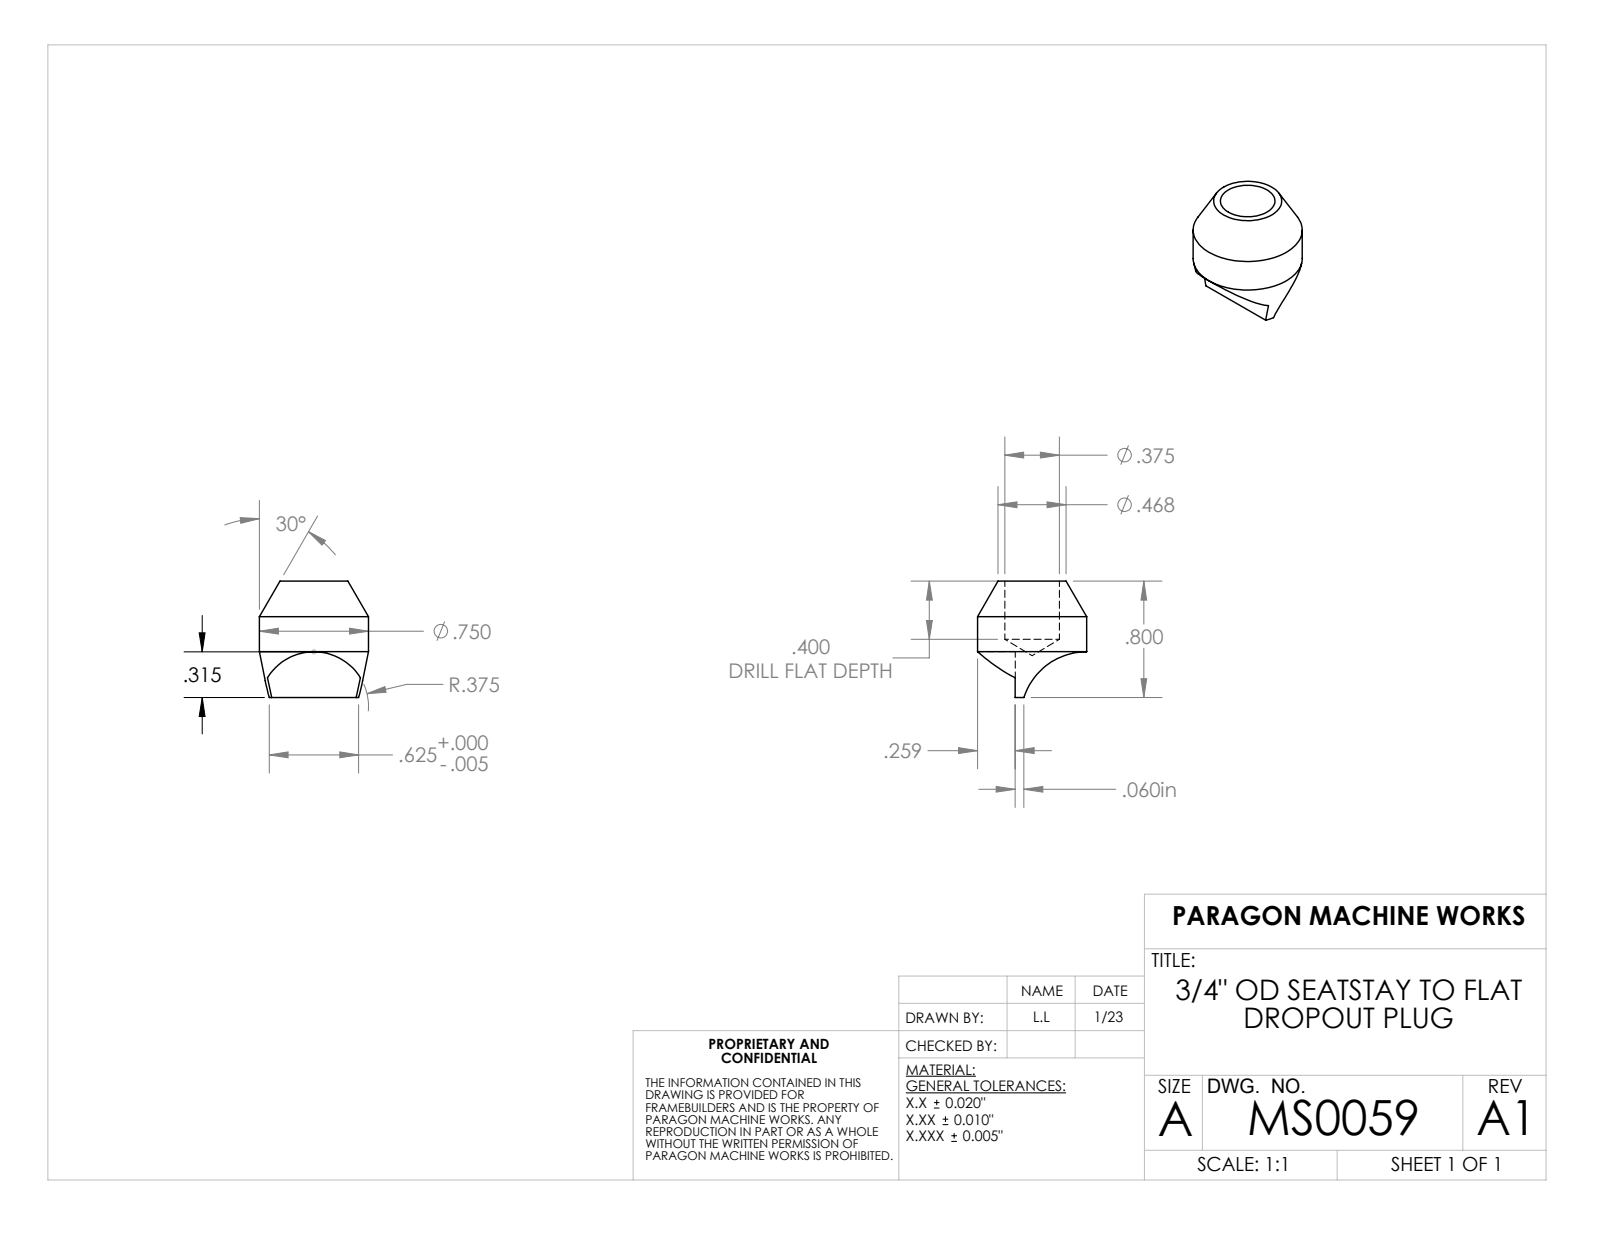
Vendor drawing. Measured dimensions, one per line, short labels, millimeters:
name: MS0059
written by: SolidWorks 2022 (AUTOMOTIVE_DESIGN)
unit: mm
bodies: 1 solid, 15 faces (3 planar, 6 cylindrical, 6 other)
size: 20.3 × 19.1 × 19.1
volume: 2 830 mm³; area: 1 695 mm²
holes: 1× ⌀9.5
bosses: 1× ⌀19.1
rounds: 1× R9.5, 1× R11.5
face distances: 20.3
